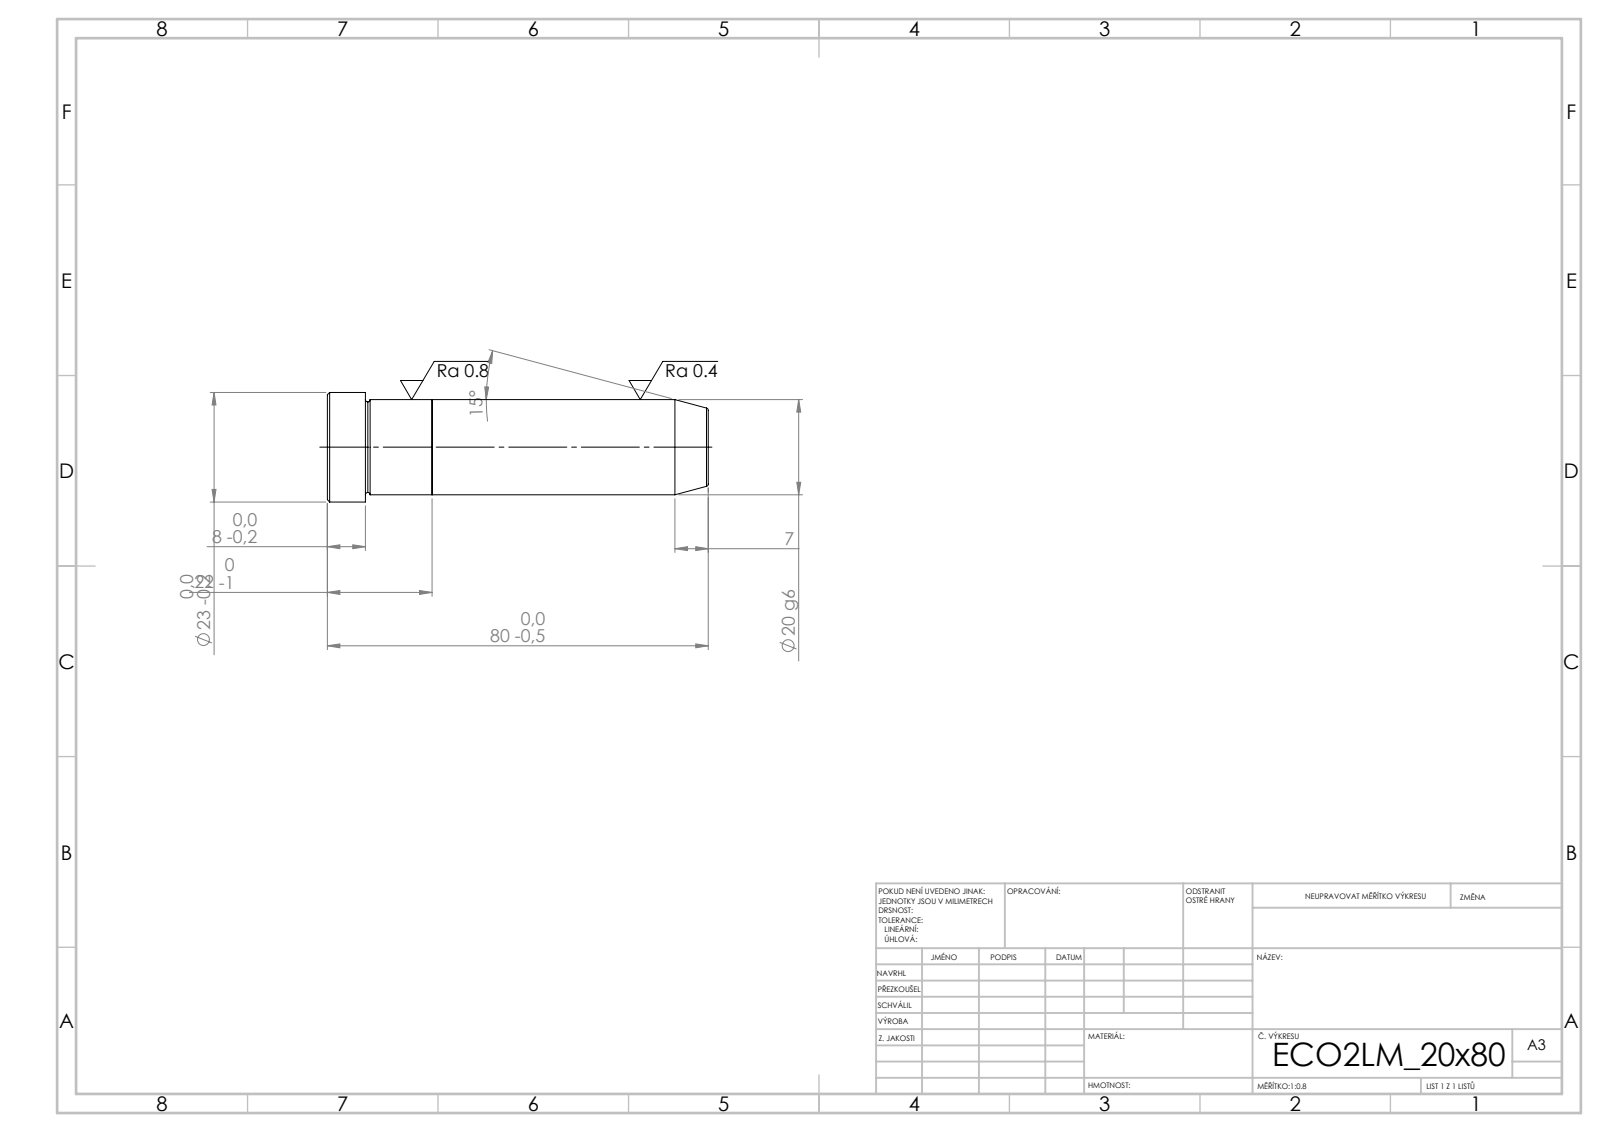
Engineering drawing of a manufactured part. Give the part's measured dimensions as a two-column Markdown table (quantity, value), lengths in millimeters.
| quantity | value |
| --- | --- |
| STEP written by | SolidWorks 2019 (CONFIG_CONTROL_DESIGN) |
| units | millimeters |
| bodies | 2 solids, 21 faces (5 planar, 6 cylindrical, 10 other) |
| overall size | 80 × 23 × 23 |
| volume | 25 522 mm³ |
| surface area | 6 433 mm² |
| round bosses / shafts (diameter × count) | 23 × 1, 20 × 1 |
| main face-to-face distances | 22, 58, 80, 72, 14, 8 |
